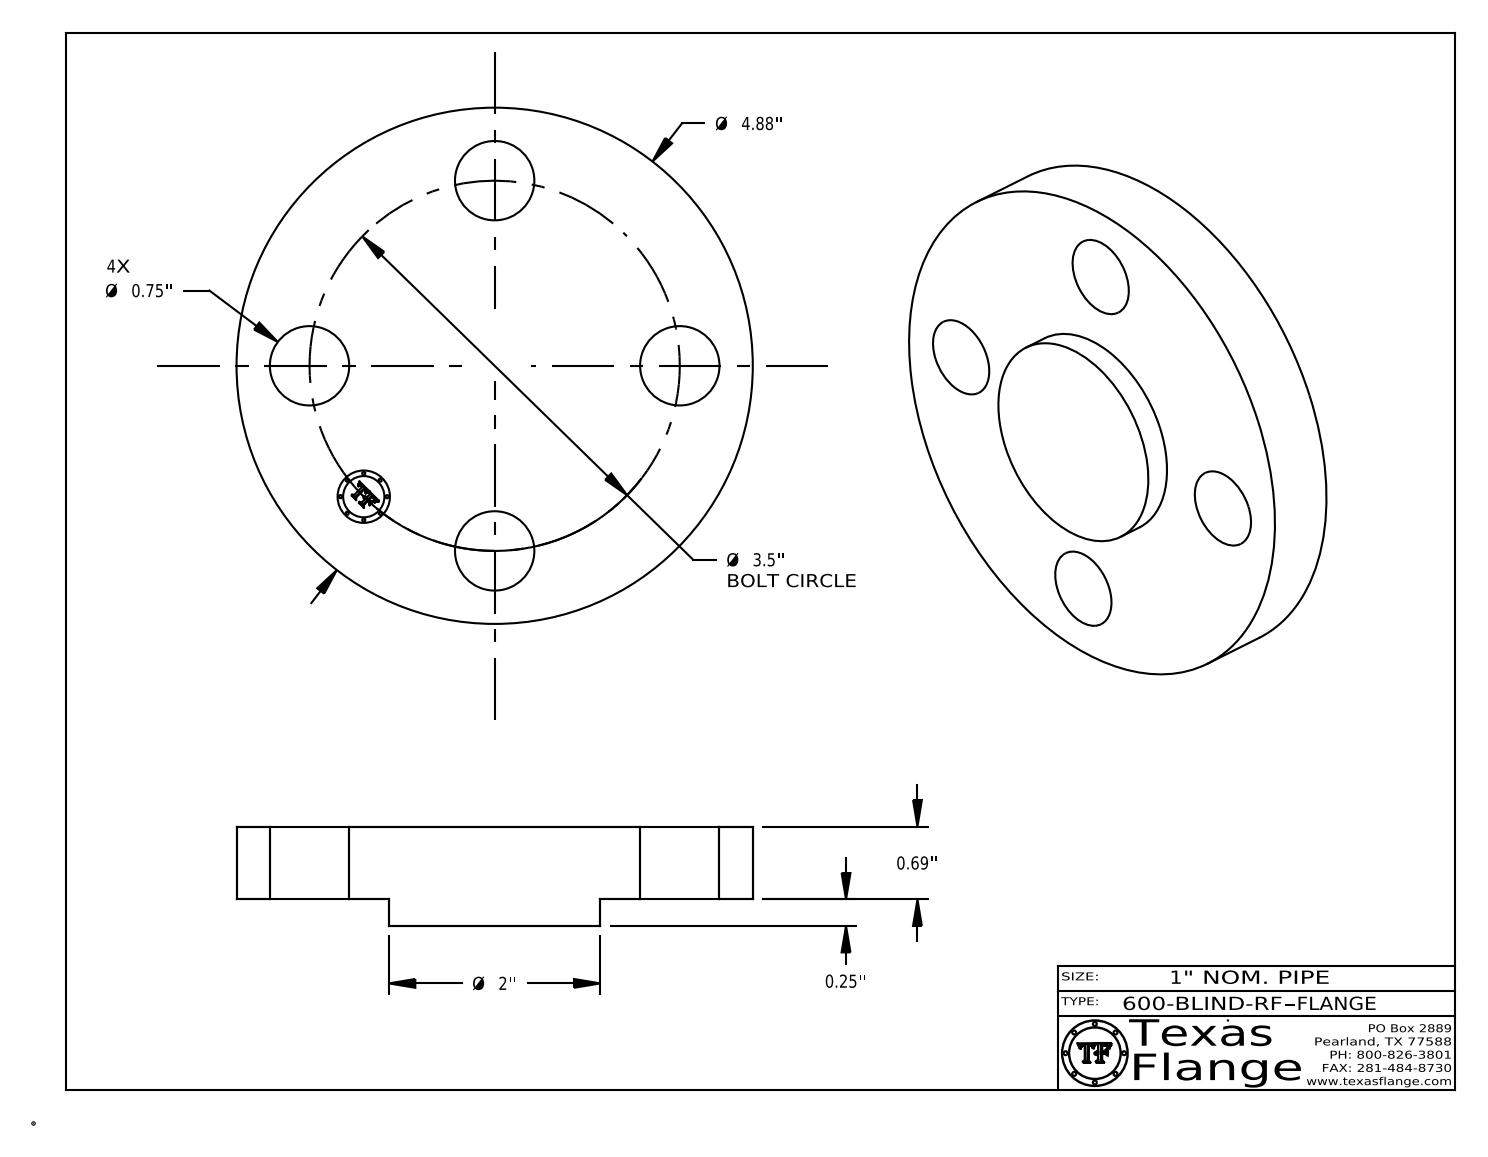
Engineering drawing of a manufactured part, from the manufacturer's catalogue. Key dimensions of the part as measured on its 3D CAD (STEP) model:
Part name (STEP PRODUCT): 600-BLIND-RF
STEP written by: CATIA V5 STEP AP214 (AUTOMOTIVE_DESIGN)
Units: inches
Bodies: 1 solid, 400 faces (368 planar, 32 cylindrical, 0 other)
Overall size (bounding box): 4.88 × 4.88 × 0.94
Volume: 12.47 in³ · Surface area: 52.62 in²
Round holes (diameter × count): ⌀0.75 ×4, ⌀0.495 ×1
Round bosses / shafts (diameter × count): ⌀0.03 ×8, ⌀4.88 ×1, ⌀2 ×1, ⌀0.39 ×1
Main face-to-face distances: 0.69, 0.25, 0.94, 0.015, 0.925, 0.675, 0.148, 0.145, 0.027, 0.096
Hole centre spacings: 2.475, 1.339, 3.233, 3.5
